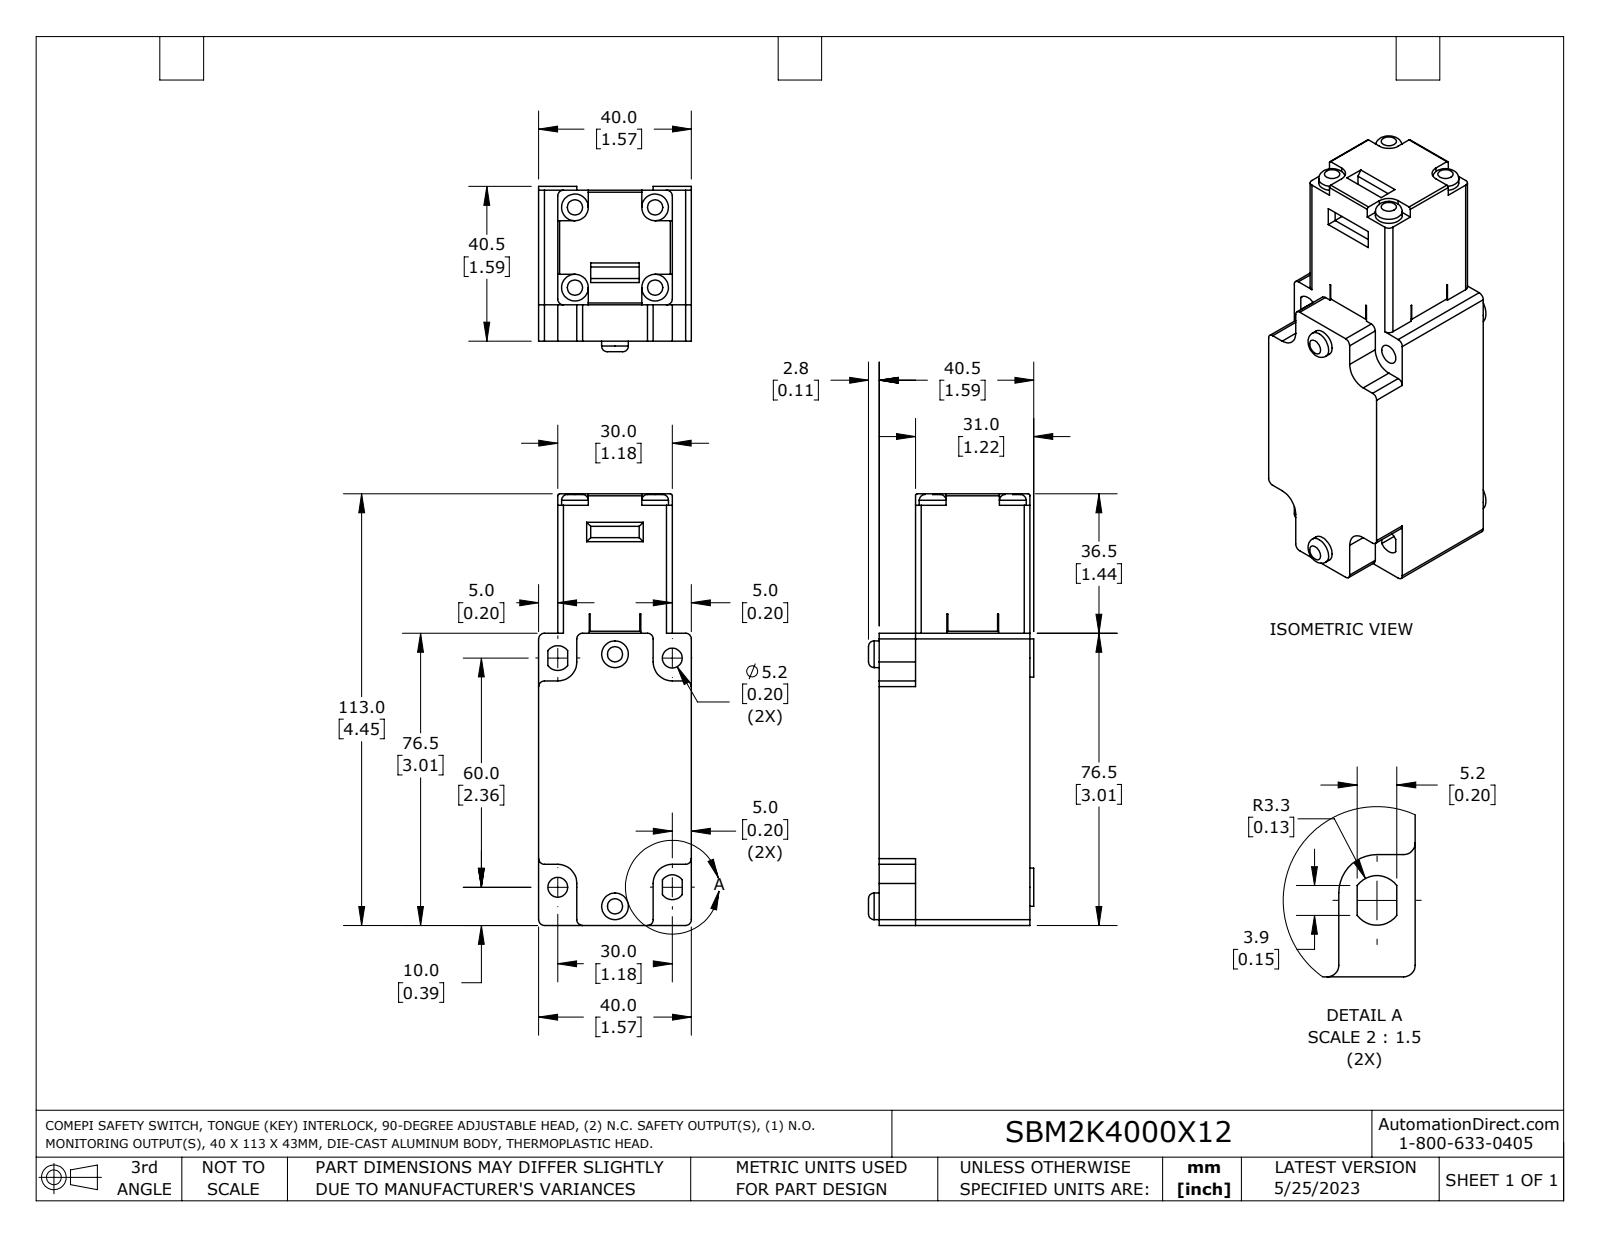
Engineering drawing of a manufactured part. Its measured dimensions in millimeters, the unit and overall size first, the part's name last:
Units: millimetres
Overall size (bounding box): 113 × 43.3 × 40
Round holes (diameter × count): ⌀7 ×4, ⌀5.2 ×2, ⌀17 ×1, ⌀19 ×1
Round bosses / shafts (diameter × count): ⌀10 ×4, ⌀7 ×2
Partial cylindrical surfaces — rounded edges, fillets, slot ends (radius × count): R1.5 ×16, R0.5 ×4, R5 ×4, R3.3 ×2, R11.5 ×1, R12 ×1
Main face-to-face distances: 30, 40, 39.5, 5, 35, 9.5, 76.5, 3, 0.5, 25
Hole centre spacings: 21, 14.1, 15.6, 29.7, 67.1
Volume: 139 400 mm³ · Surface area: 25 930 mm²
Bodies: 1 solid, 147 faces (86 planar, 54 cylindrical, 7 other)
Part name (STEP PRODUCT): SBM2K4000X12
STEP written by: SolidWorks 2021 (AUTOMOTIVE_DESIGN)
